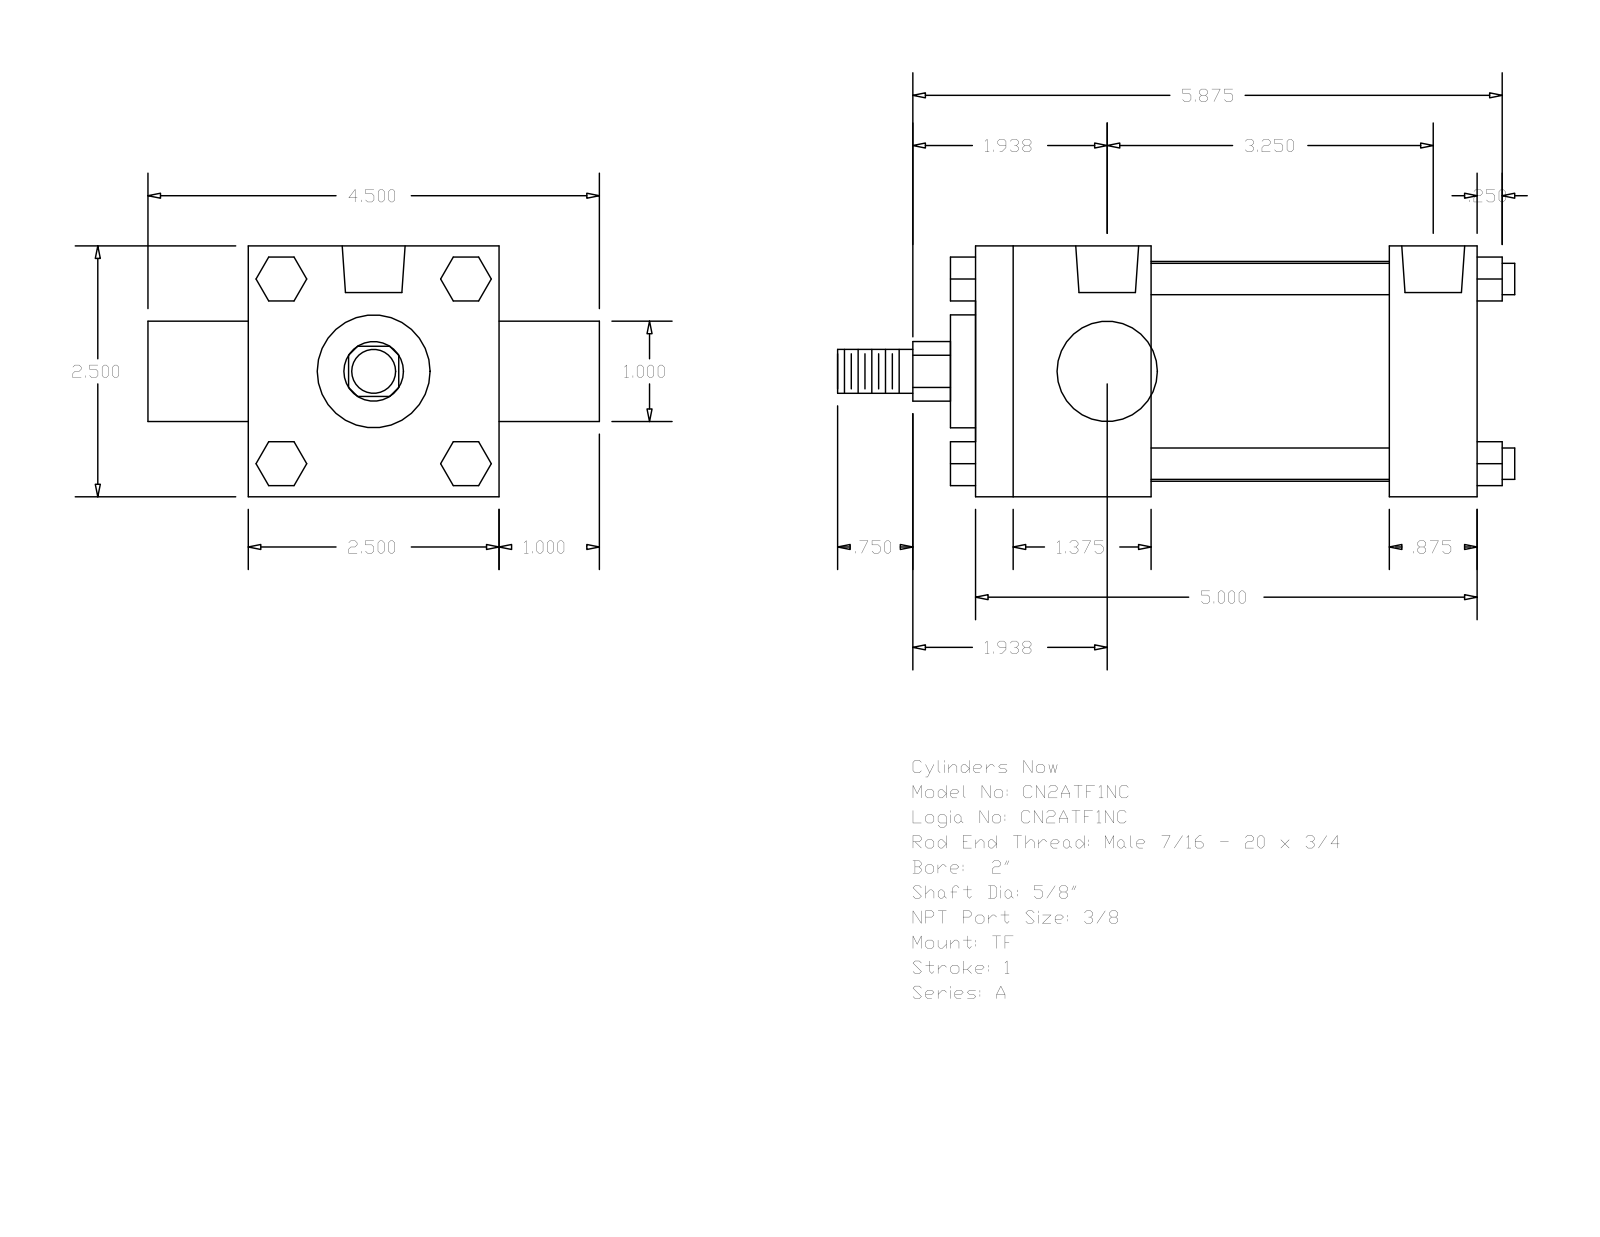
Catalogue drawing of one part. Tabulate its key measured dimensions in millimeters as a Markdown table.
| quantity | value |
| --- | --- |
| part name | A_TF__0200_0.625 |
| STEP written by | GSSL Pune (CONFIG_CONTROL_DESIGN) |
| units | millimeters |
| bodies | 0 solids, 120 faces (92 planar, 28 cylindrical, 0 other) |
| overall size | 171.45 × 114.3 × 63.5 |
| round holes (diameter × count) | 5.56 × 3, 15.93 × 2 |
| round bosses / shafts (diameter × count) | 7.94 × 4, 55.63 × 1, 28.57 × 1, 25.4 × 1, 15.88 × 1, 11.11 × 1 |
| partial cylindrical surfaces (radius × count) | 7.54 × 1 |
| main face-to-face distances | 63.5, 127, 44.45, 104.77, 60.32, 82.55, 22.23, 25.4, 88.9, 50.8 |
| hole center spacings | 3.97, 3.98, 74.6, 78.57, 78.58, 82.55 |
